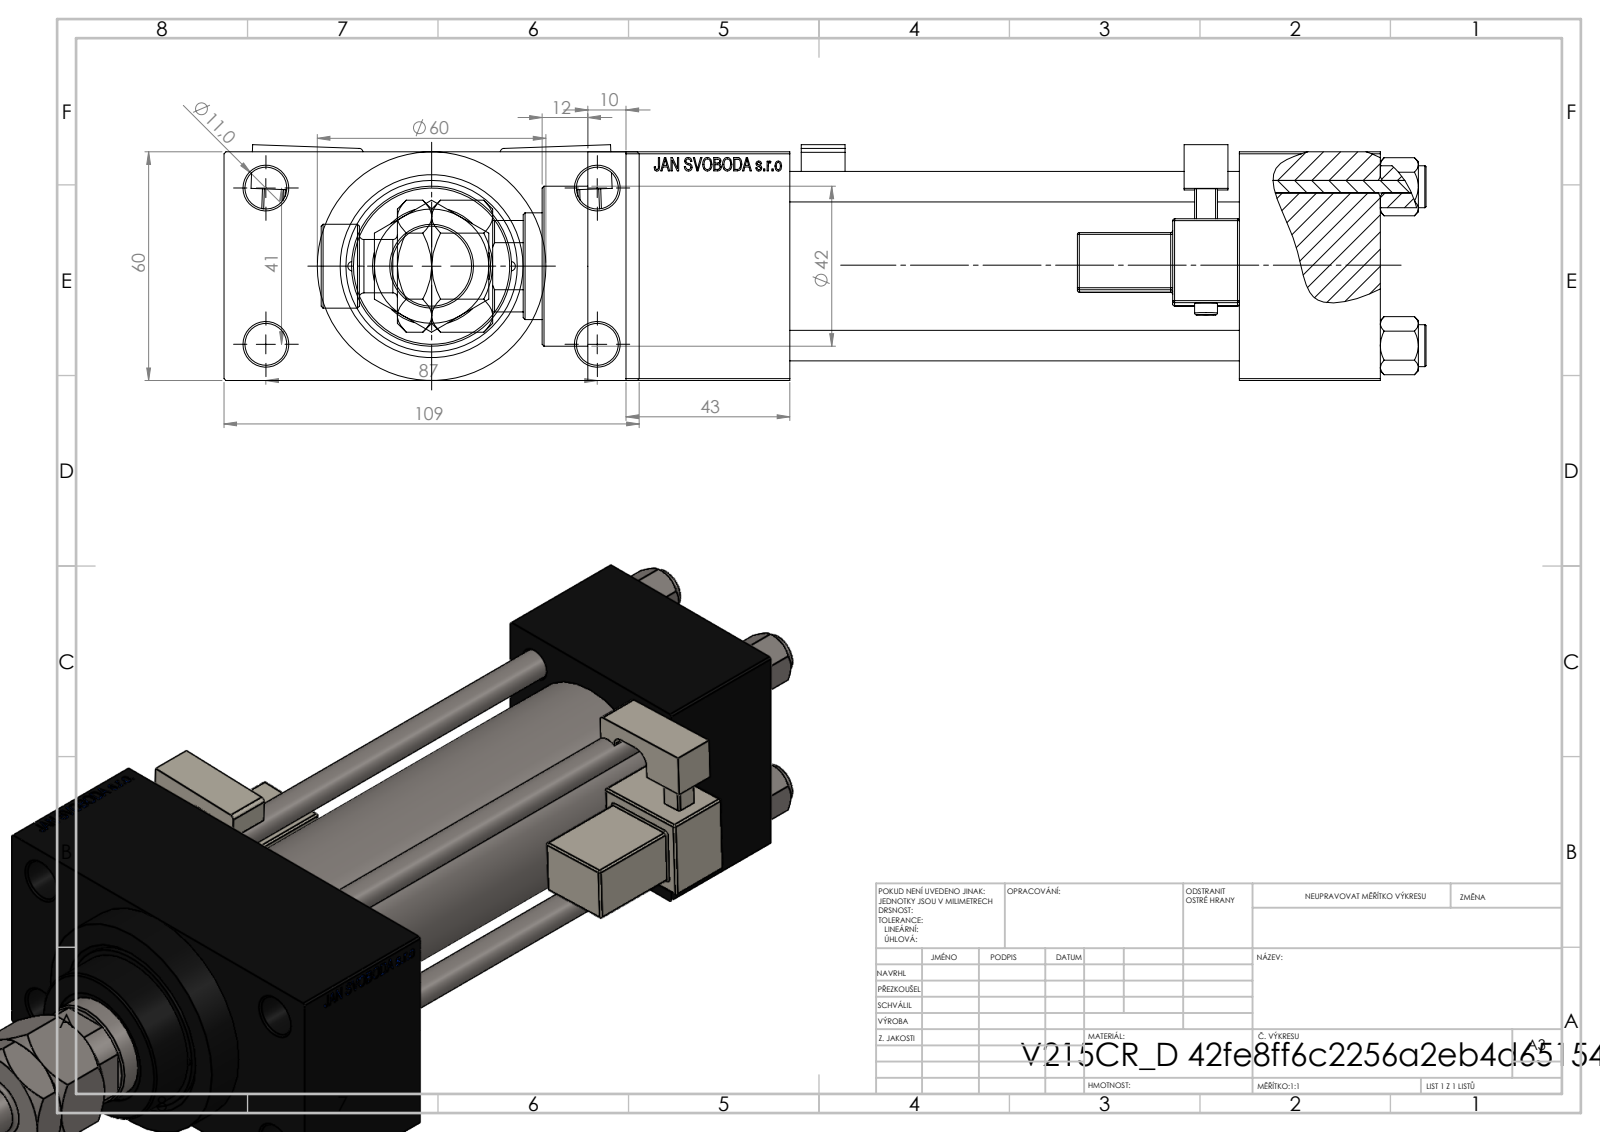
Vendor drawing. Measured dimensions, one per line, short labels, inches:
name: V215CR_D_Body; V215CR_VCP_D; V215_VC_A; MFA (+3 more)
written by: SolidWorks 2019 (CONFIG_CONTROL_DESIGN)
unit: in
bodies: 14 solids, 1320 faces (576 planar, 156 cylindrical, 588 other)
size: 11.417 × 4.291 × 2.437
volume: 40.73 in³; area: 270.1 in²
holes: 4× ⌀0.315, 4× ⌀0.433, 2× ⌀0.098, 2× ⌀0.276, 2× ⌀0.656, 2× ⌀0.945, 1× ⌀0.728, 1× ⌀1.102, 1× ⌀1.22, 1× ⌀1.575, 1× ⌀1.772
bosses: 4× ⌀0.433, 2× ⌀0.236, 1× ⌀2.362, 1× ⌀1.811, 1× ⌀1.654, 1× ⌀0.866, 1× ⌀0.551
rounds: 48× R0.02, 2× R0.039, 2× R0.098, 2× R0.157, 1× R0.531
face distances: 2.362, 4.646, 0.965, 3.327, 1.457, 6.102, 7.795, 6.339, 1.693, 4.291
hole spacings: 0.821, 0.892, 1.161, 1.206, 1.642, 1.832, 1.856, 1.893
